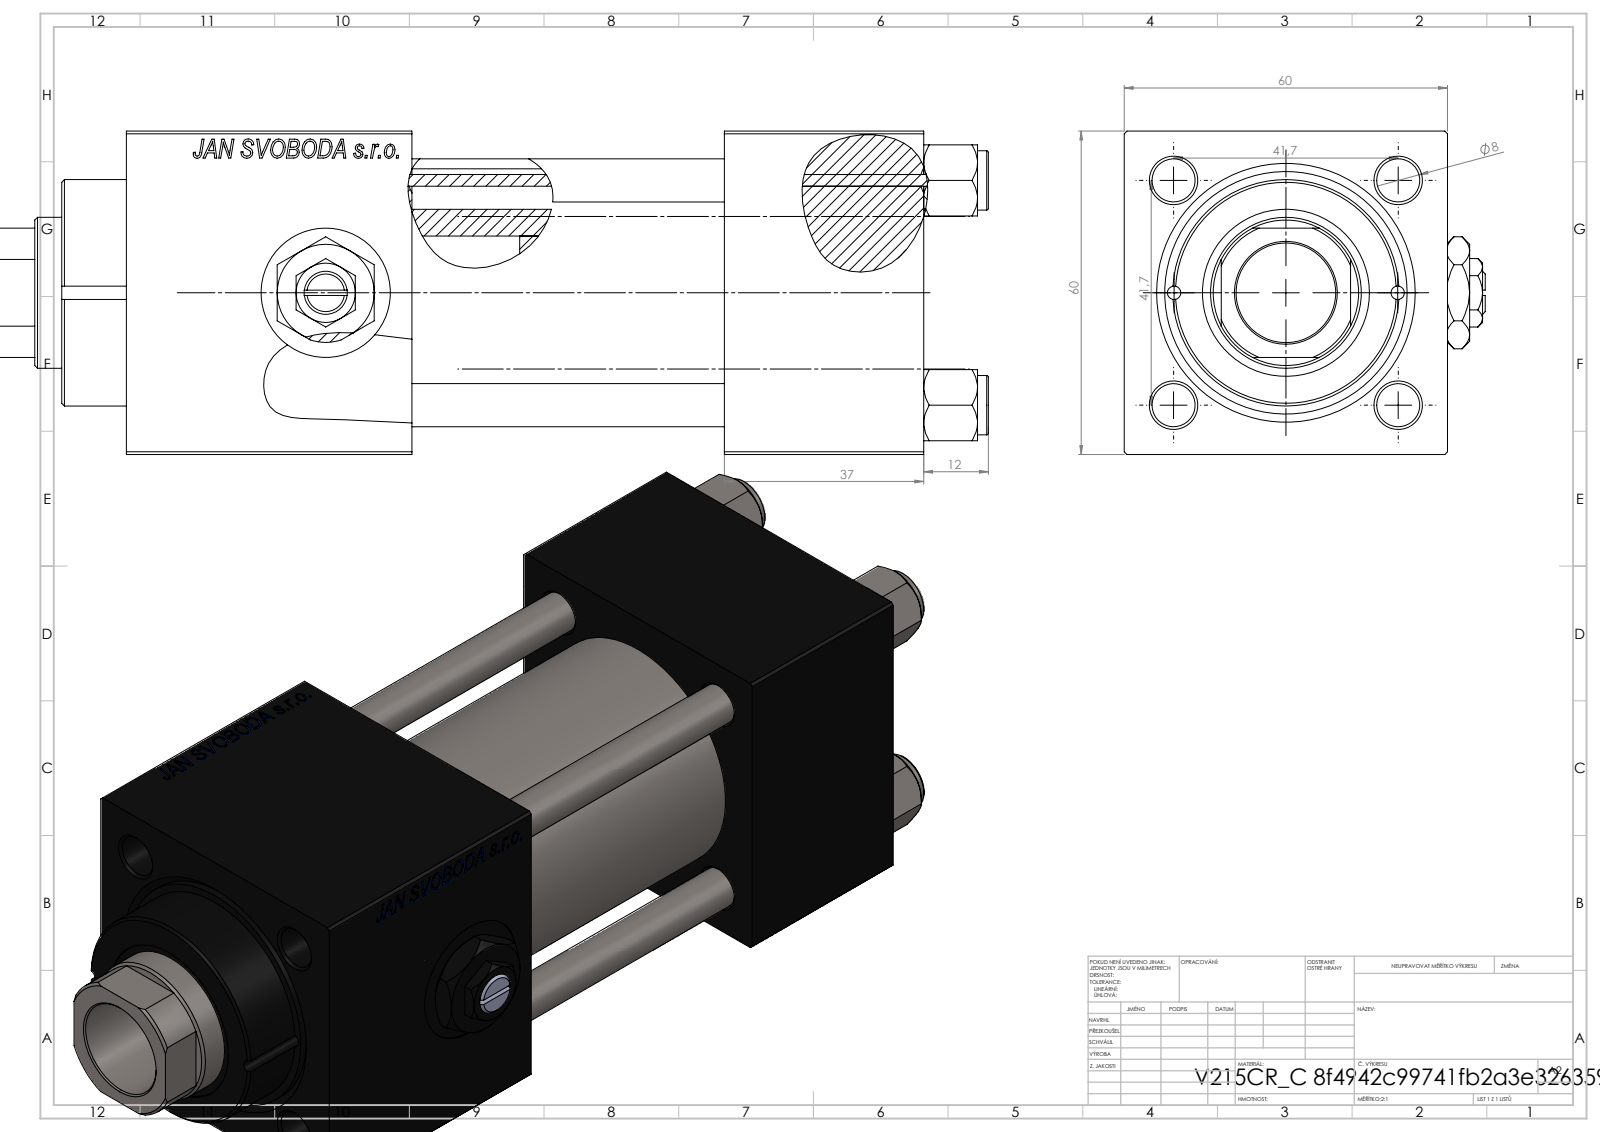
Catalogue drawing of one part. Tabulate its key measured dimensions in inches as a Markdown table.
| quantity | value |
| --- | --- |
| part name | V215CR_C_Body; V215_VC_A; V215CR_VCP_C; V215CR_C_TYCINKA (+2 more) |
| STEP written by | SolidWorks 2019 (CONFIG_CONTROL_DESIGN) |
| units | inches |
| bodies | 12 solids, 1202 faces (552 planar, 94 cylindrical, 556 other) |
| overall size | 7.283 × 2.638 × 2.362 |
| volume | 25.76 in³ |
| surface area | 174.9 in² |
| round holes (diameter × count) | 0.315 × 4, 0.098 × 2, 0.276 × 2, 0.656 × 2, 0.945 × 2, 0.728 × 1, 1.102 × 1, 1.22 × 1, 1.575 × 1, 1.772 × 1 |
| round bosses / shafts (diameter × count) | 0.433 × 4, 1.811 × 1, 1.654 × 1 |
| partial cylindrical surfaces (radius × count) | 0.531 × 1 |
| main face-to-face distances | 2.362, 1.457, 2.283, 3.74, 2.087, 4.697, 3.24, 0.957, 5.827, 4.37 |
| hole center spacings | 0.821, 1.161, 1.642, 1.832, 0.817, 2.322, 1.634, 3.642 |
